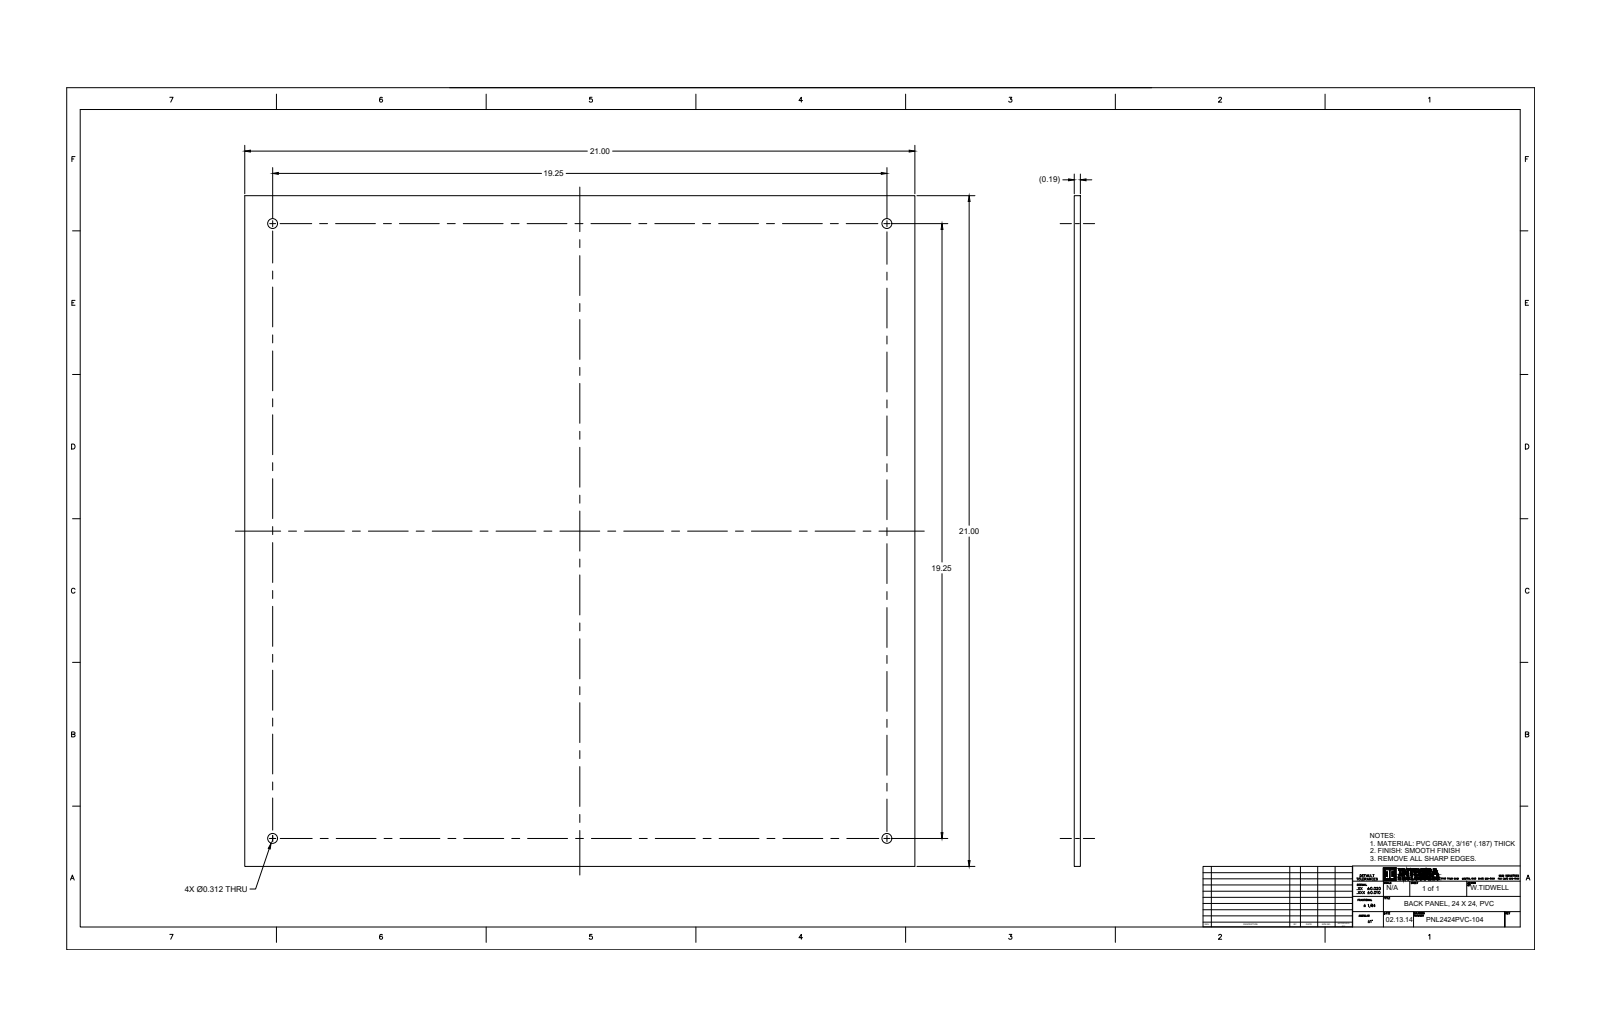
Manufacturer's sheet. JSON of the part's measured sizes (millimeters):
{"part_name": "PVCBP-2424-P10", "step_written_by": "SolidWorks 2018 (AUTOMOTIVE_DESIGN)", "units": "millimeters", "bodies": {"solids": 1, "faces": 10, "planar": 6, "cylindrical": 4, "other": 0}, "overall_size": [533.4, 533.4, 4.7], "volume_mm3": 1350000, "surface_area_mm2": 579200, "round_holes": [[7.9, 4]], "face_to_face_distances": [4.7, 533.4], "hole_center_spacings": [489, 691.5]}
